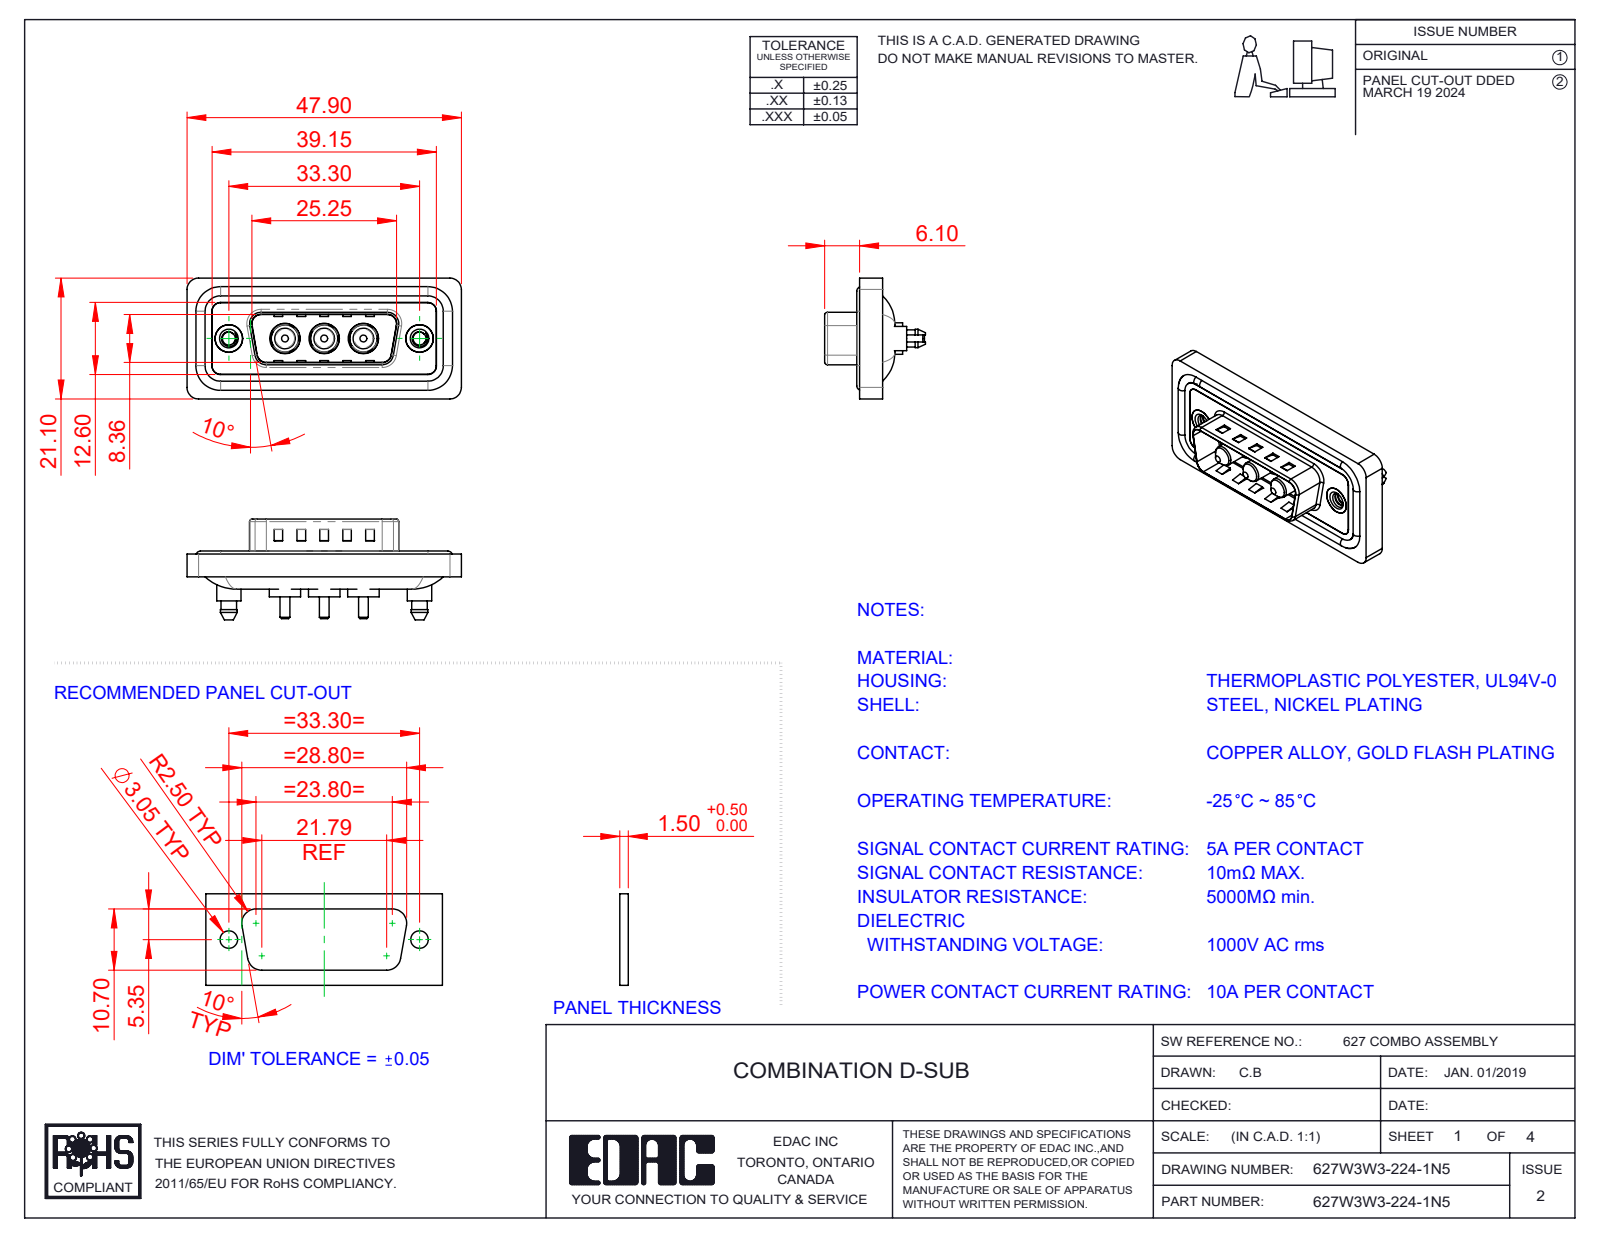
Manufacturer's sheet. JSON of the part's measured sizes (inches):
{"part_name": "627W3W3-224-1N5; 627Combo Threaded Boardlock_5; 627Combo Housing_3W3; 627Combo Shell Front_15 Contacts (+3 more)", "step_written_by": "SolidWorks 2023 (CONFIG_CONTROL_DESIGN)", "units": "inches", "bodies": {"solids": 13, "faces": 614, "planar": 223, "cylindrical": 273, "other": 118}, "overall_size": [1.886, 0.831, 0.693], "volume_in3": 0.346, "surface_area_in2": 14.03, "round_holes": [[0.191, 3], [0.209, 3], [0.089, 2], [0.157, 2], [0.189, 2], [0.197, 2]], "round_bosses_or_shafts": [[0.063, 4], [0.217, 3], [0.205, 3], [0.187, 3], [0.148, 3], [0.142, 3], [0.067, 3], [0.213, 2]], "partial_cylinders_radius": [[0.059, 28], [0.079, 20], [0.063, 10], [0.02, 8], [0.01, 4], [0.024, 4], [0.026, 4], [0.035, 4]], "face_to_face_distances": [0.016, 0.059, 0.043, 0.063, 0.02, 0.122, 0.114, 0.157, 0.028, 0.032], "hole_center_spacings": [0.27, 0.386, 0.656, 0.925, 0.539, 1.311]}
